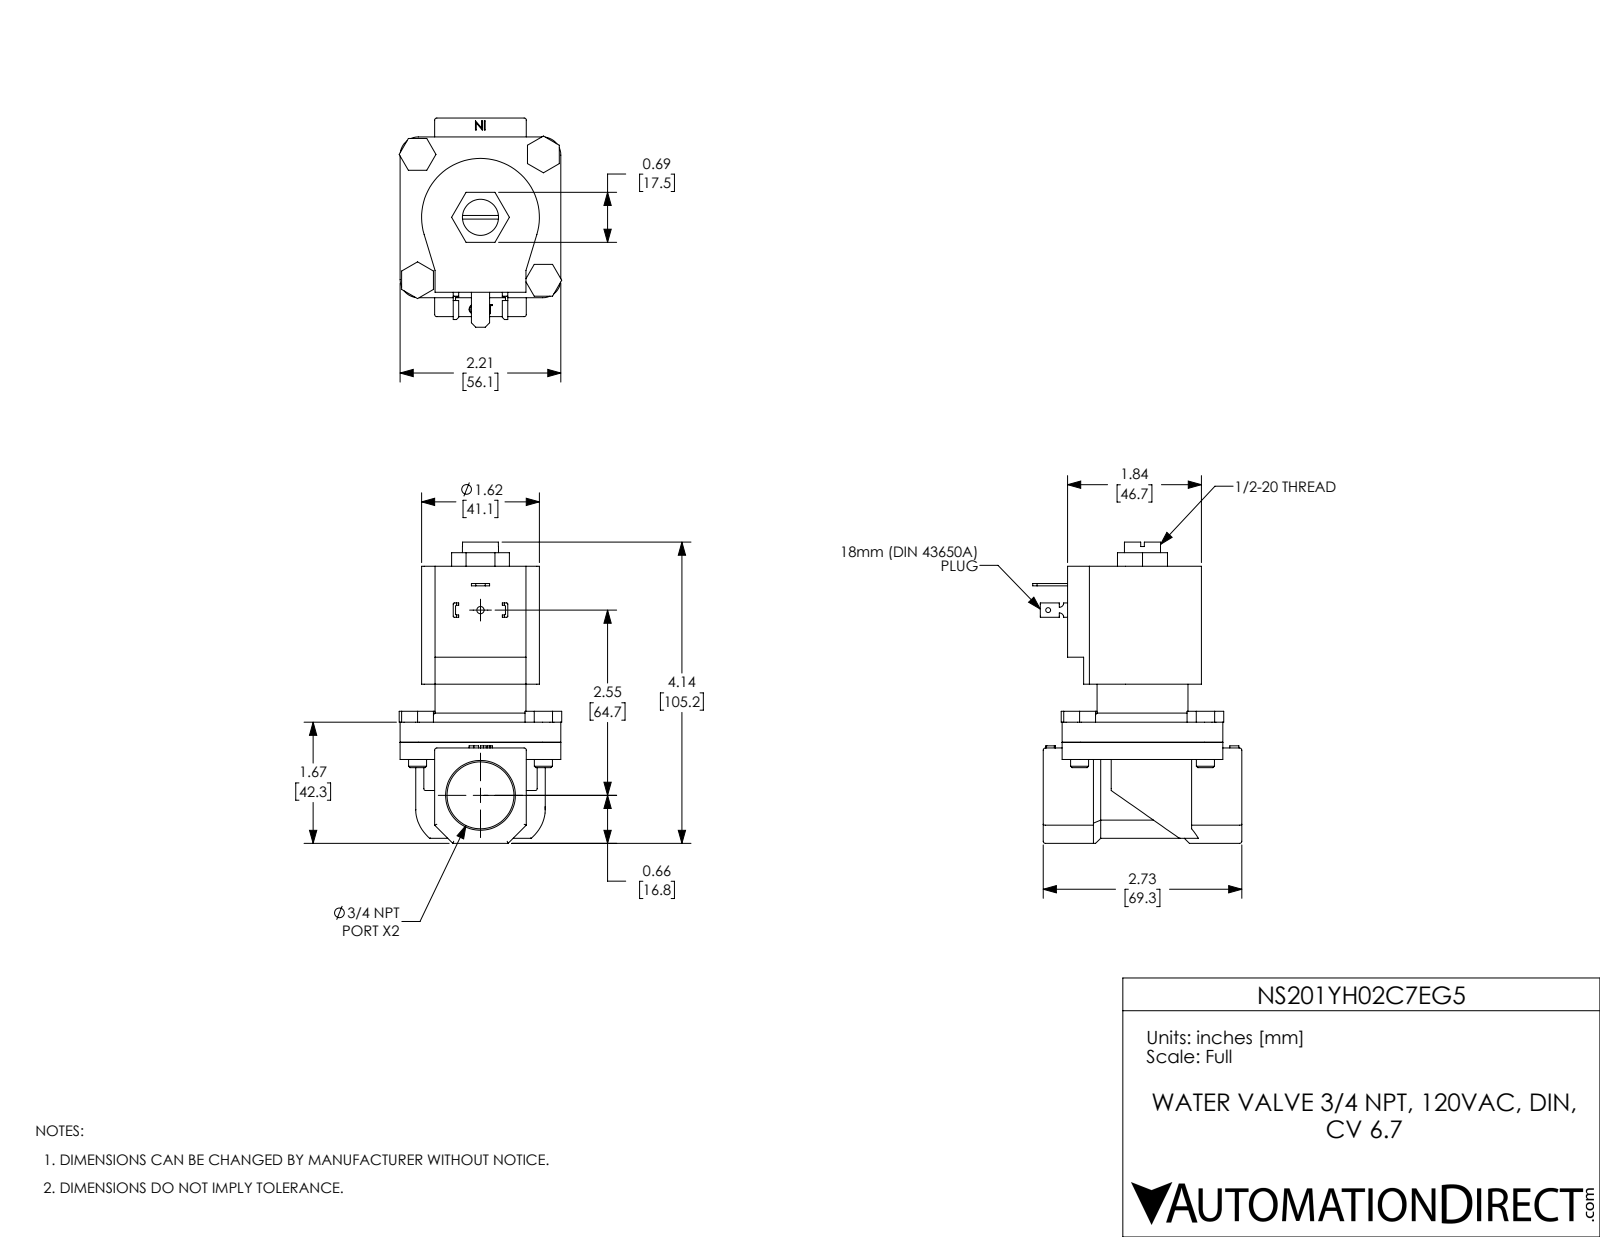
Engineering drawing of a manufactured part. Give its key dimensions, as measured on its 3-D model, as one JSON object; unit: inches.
{"part_name": "NS201YH02C7EG5", "step_written_by": "SolidWorks 2024 (CONFIG_CONTROL_DESIGN)", "units": "inches", "bodies": {"solids": 11, "faces": 332, "planar": 198, "cylindrical": 99, "other": 35}, "overall_size": [4.14, 2.875, 2.235], "volume_in3": 10.32, "surface_area_in2": 67.12, "round_holes": [[0.25, 4], [0.067, 1], [0.1, 1], [0.496, 1], [0.512, 1], [0.92, 1], [1.155, 1]], "round_bosses_or_shafts": [[0.248, 4], [1.25, 1]], "partial_cylinders_radius": [[0.03, 15], [0.015, 8], [0.25, 4], [0.06, 2], [0.81, 1], [0.89, 1]], "face_to_face_distances": [0.276, 2.419, 2.143, 0.475, 1.735, 2.21, 0.236, 0.512, 2.655, 0.26], "hole_center_spacings": [1.223, 1.73, 2.446, 2.546]}
